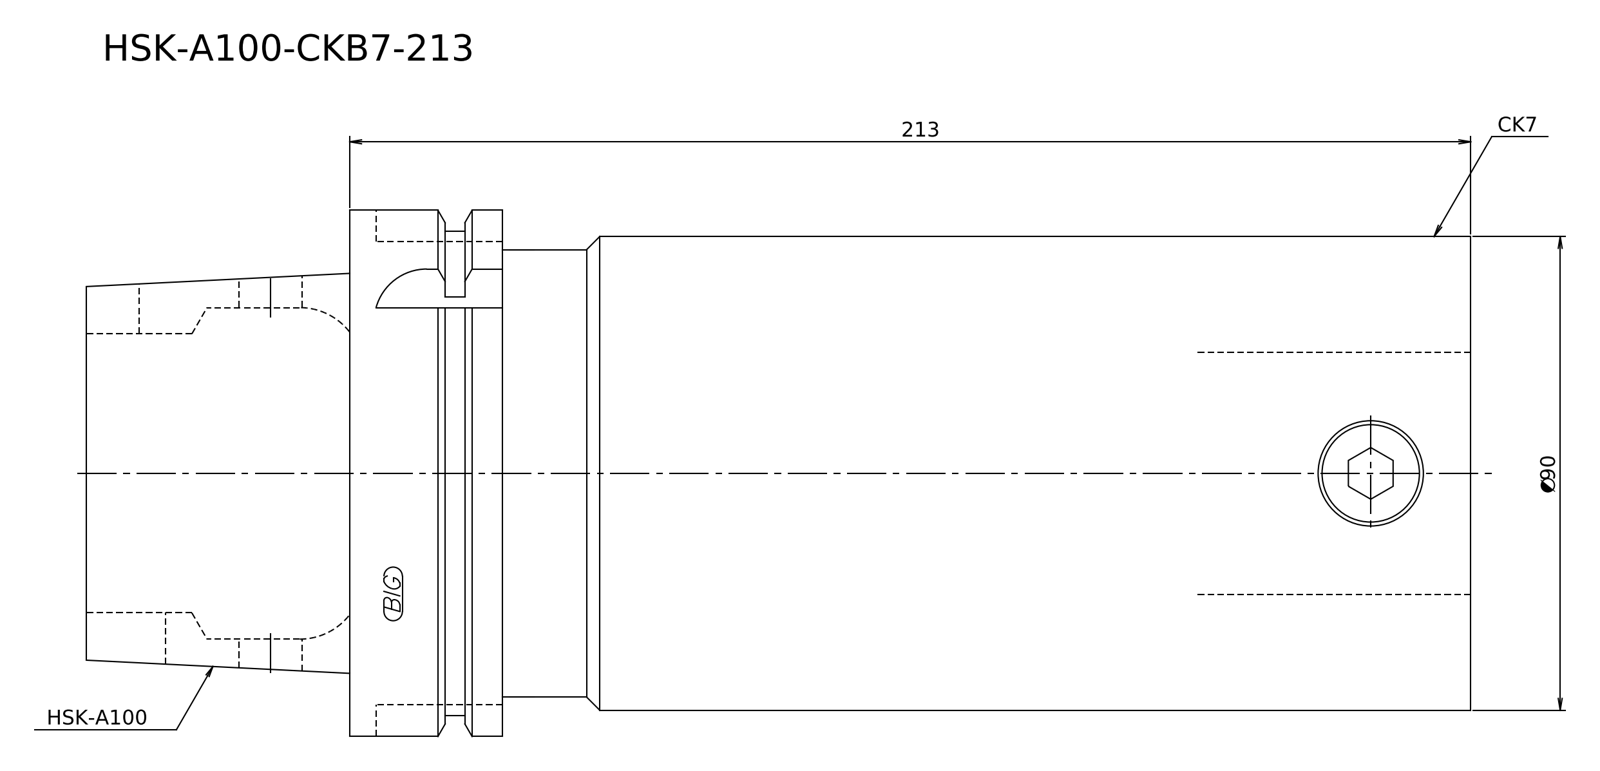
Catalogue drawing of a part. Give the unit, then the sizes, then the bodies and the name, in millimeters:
Units: millimetres
Overall size (bounding box): 263 × 100 × 100
Round bosses / shafts (diameter × count): ⌀100 ×1, ⌀92 ×1, ⌀90 ×1, ⌀83.4 ×1, ⌀75.8 ×1
Main face-to-face distances: 263, 213, 50, 184, 29, 79, 191.12, 7.12, 21.88, 71.88
Volume: 1 590 000 mm³ · Surface area: 90 573 mm²
Bodies: 1 solid, 17 faces (7 planar, 6 cylindrical, 4 other)
STEP written by: Kubotek KeyCreator 2011 V10.0.2 (22737) (automotive_design)
